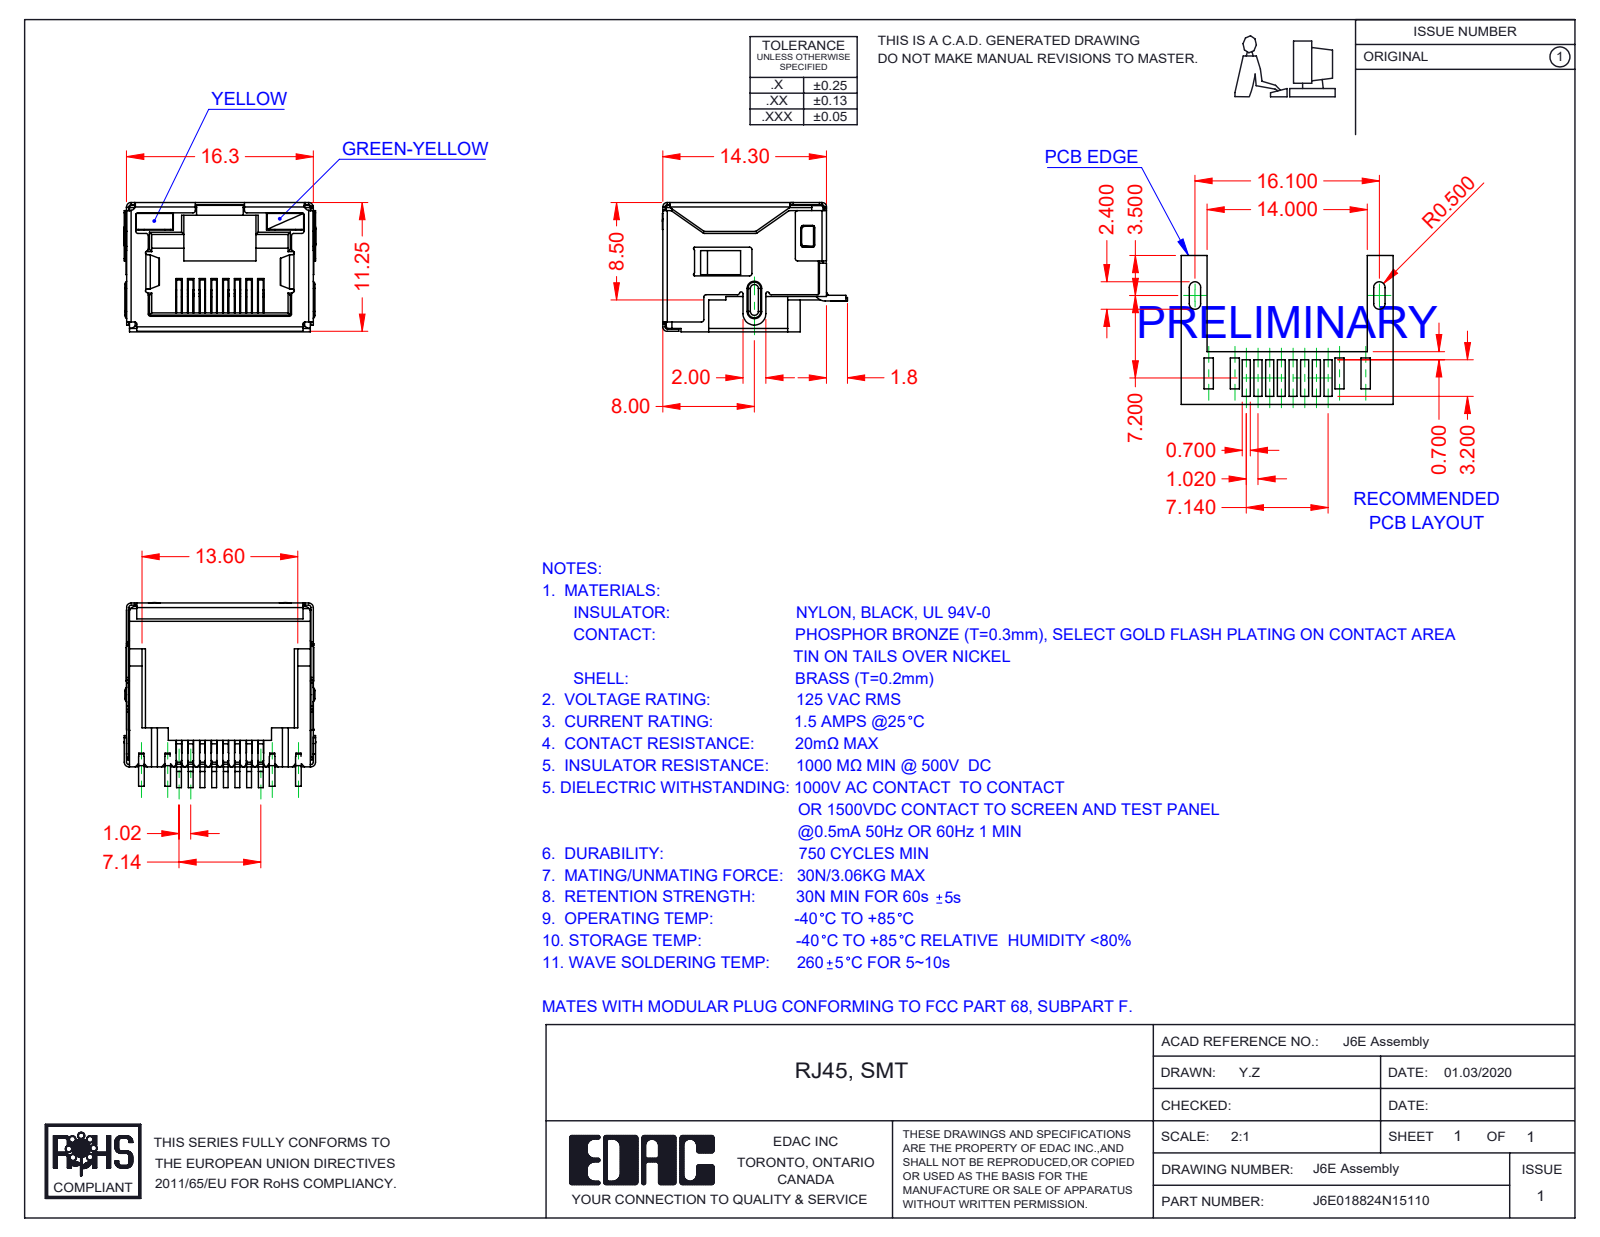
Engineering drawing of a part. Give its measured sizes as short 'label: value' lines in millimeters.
name: 6E LED LH_1-Yellow; 6E Shield_LED; J6E018824N15110; 6E Contacts (+2 more)
written by: SolidWorks 2016 (CONFIG_CONTROL_DESIGN)
unit: mm
bodies: 12 solids, 1498 faces (1099 planar, 349 cylindrical, 50 other)
size: 16.75 × 16.15 × 11.3
volume: 1 109 mm³; area: 4 045 mm²
rounds: 82× R0.2, 17× R0.25, 13× R0.4, 13× R0.5, 10× R0.1, 7× R0.15, 4× R0.3, 3× R1
face distances: 11.05, 16.05, 16.1, 15.85, 11.1, 11.3, 2.4, 0.7, 9.85, 0.49
